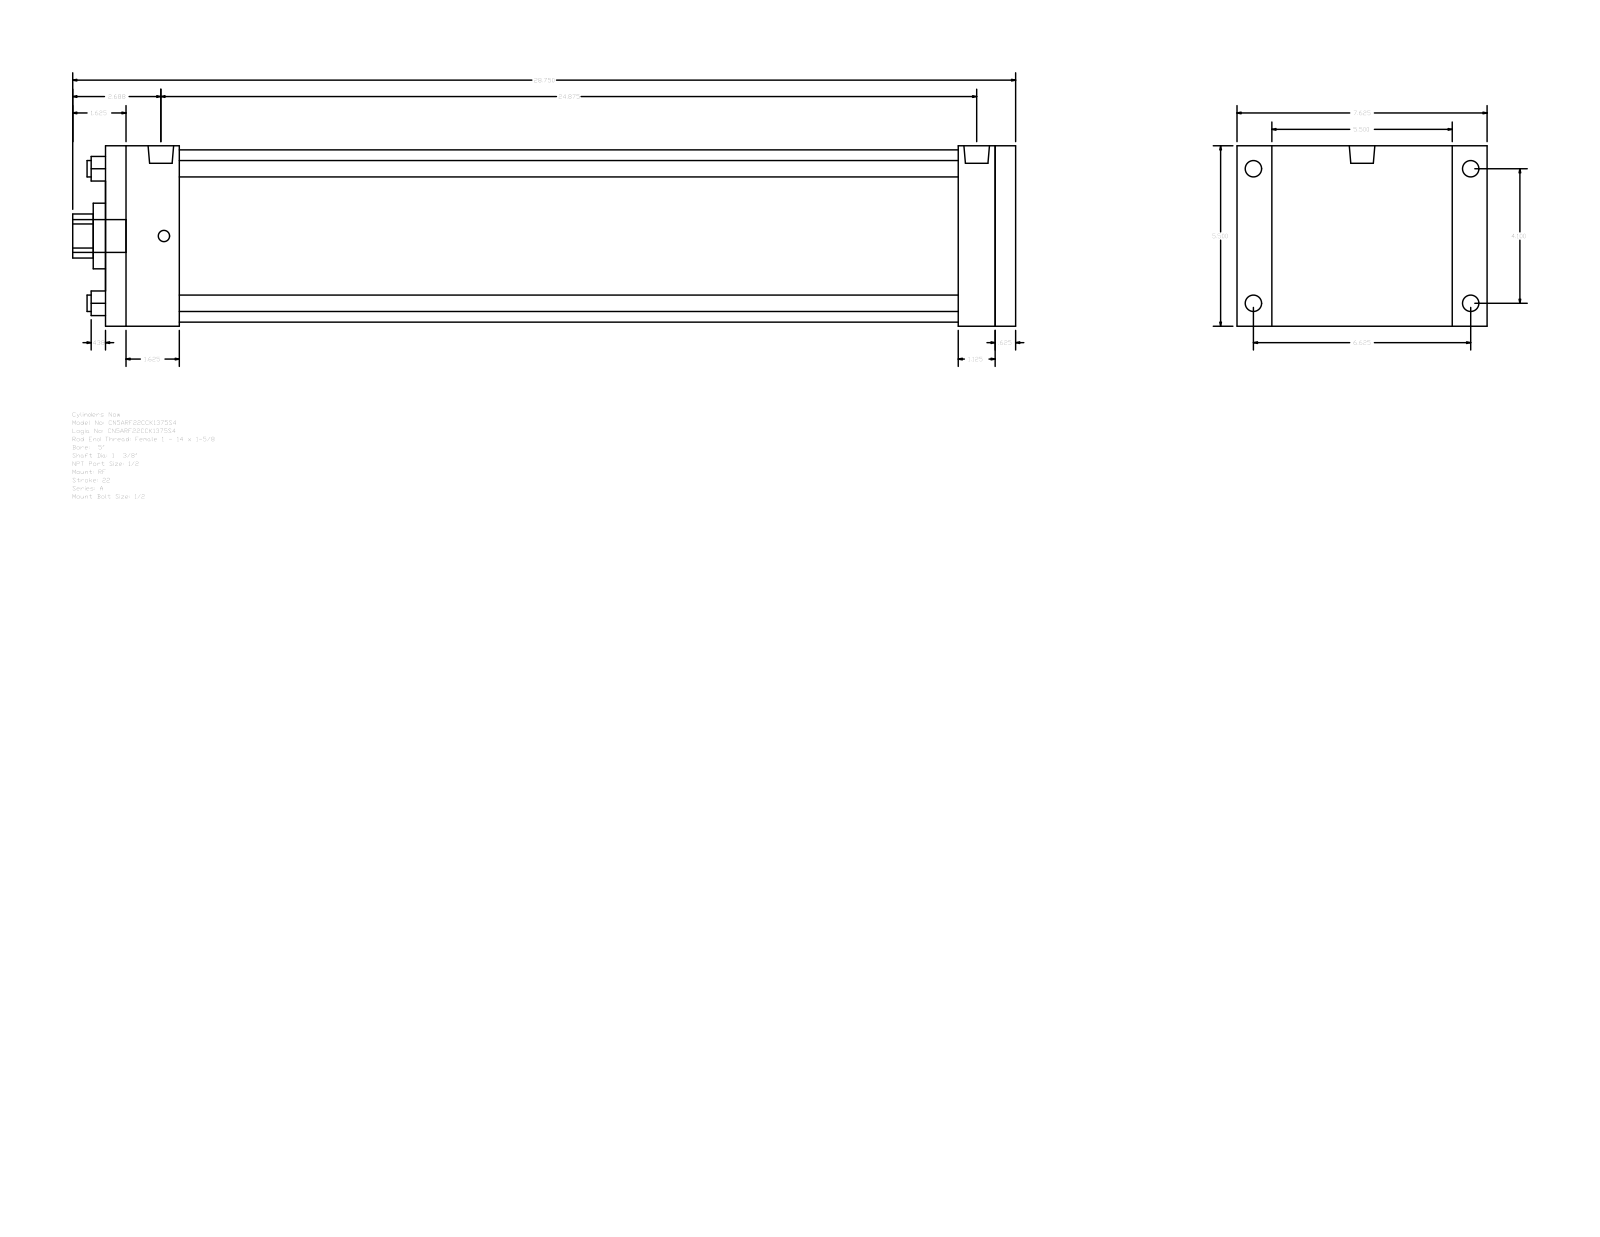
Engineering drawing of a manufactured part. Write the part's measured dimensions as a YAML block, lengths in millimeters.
part_name: "A_RF__0500_1.375"
step_written_by: "GSSL Pune (CONFIG_CONTROL_DESIGN)"
units: millimeters
bodies: {solids: 0, faces: 92, planar: 64, cylindrical: 28, other: 0}
overall_size: [730.25, 193.68, 139.7]
round_holes:
  - {diameter: 12.7, count: 4}
  - {diameter: 34.92, count: 1}
  - {diameter: 50.8, count: 1}
  - {diameter: 133.35, count: 1}
round_bosses_or_shafts:
  - {diameter: 12.7, count: 4}
  - {diameter: 8.73, count: 4}
  - {diameter: 19.77, count: 2}
  - {diameter: 25.4, count: 1}
partial_cylinders:
  - {radius: 17.06, count: 1}
face_to_face_distances: [139.7, 704.85, 15.87, 688.98, 28.58, 57.15, 631.83, 647.7, 660.4, 603.25]
hole_center_spacings: [73.64, 104.14, 147.28]
